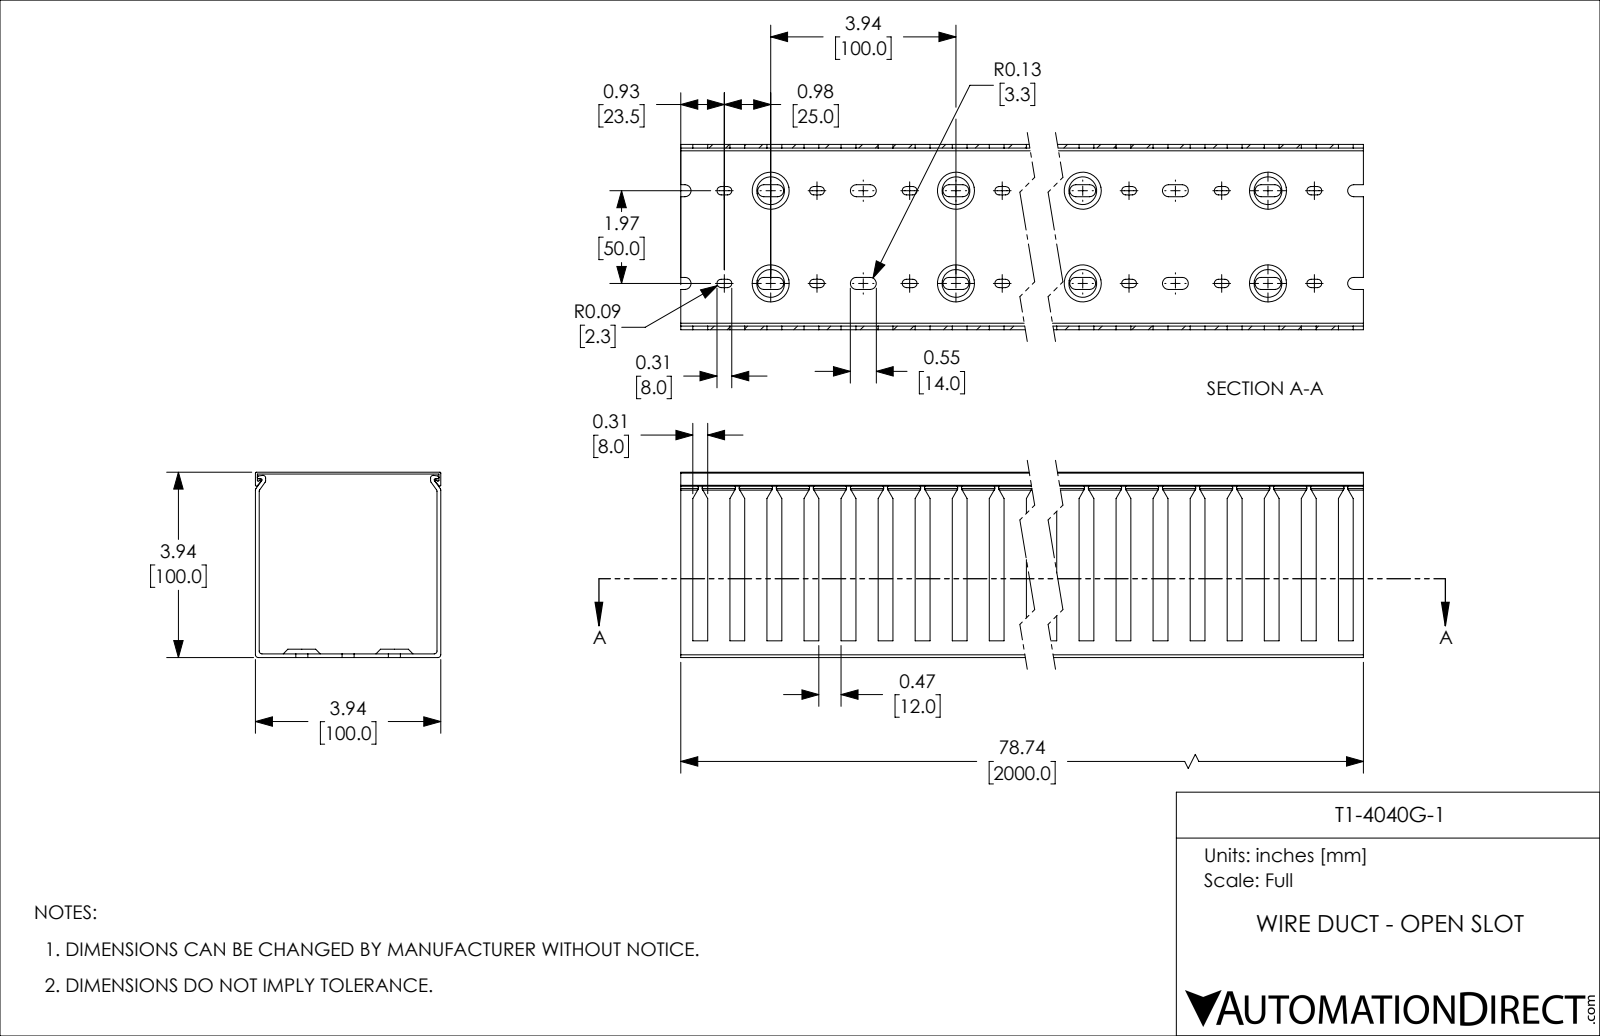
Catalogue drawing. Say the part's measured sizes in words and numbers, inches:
The part is named "T1-4040G-1". Its 3-D file was written by "SolidWorks 2021 (CONFIG_CONTROL_DESIGN)". It is 2 solids with 1573 faces: 762 planar, 731 cylindrical and 80 other. Overall it measures 78.74 by 3.937 by 3.937 inches. Its volume is 85.31 cubic inches and its surface area 2 540 square inches. Partial cylindrical surfaces (rounded edges, fillets, slot ends): 200 of radius 0.128, 160 of radius 0.089, 12 of radius 0.059, 8 of radius 0.02, 6 of radius 0.03. The main face-to-face distances are 0.079, 3.858, 3.937, 0.039, 3.898, 3.819, 3.78, 0.177, 3.72, 0.217.
